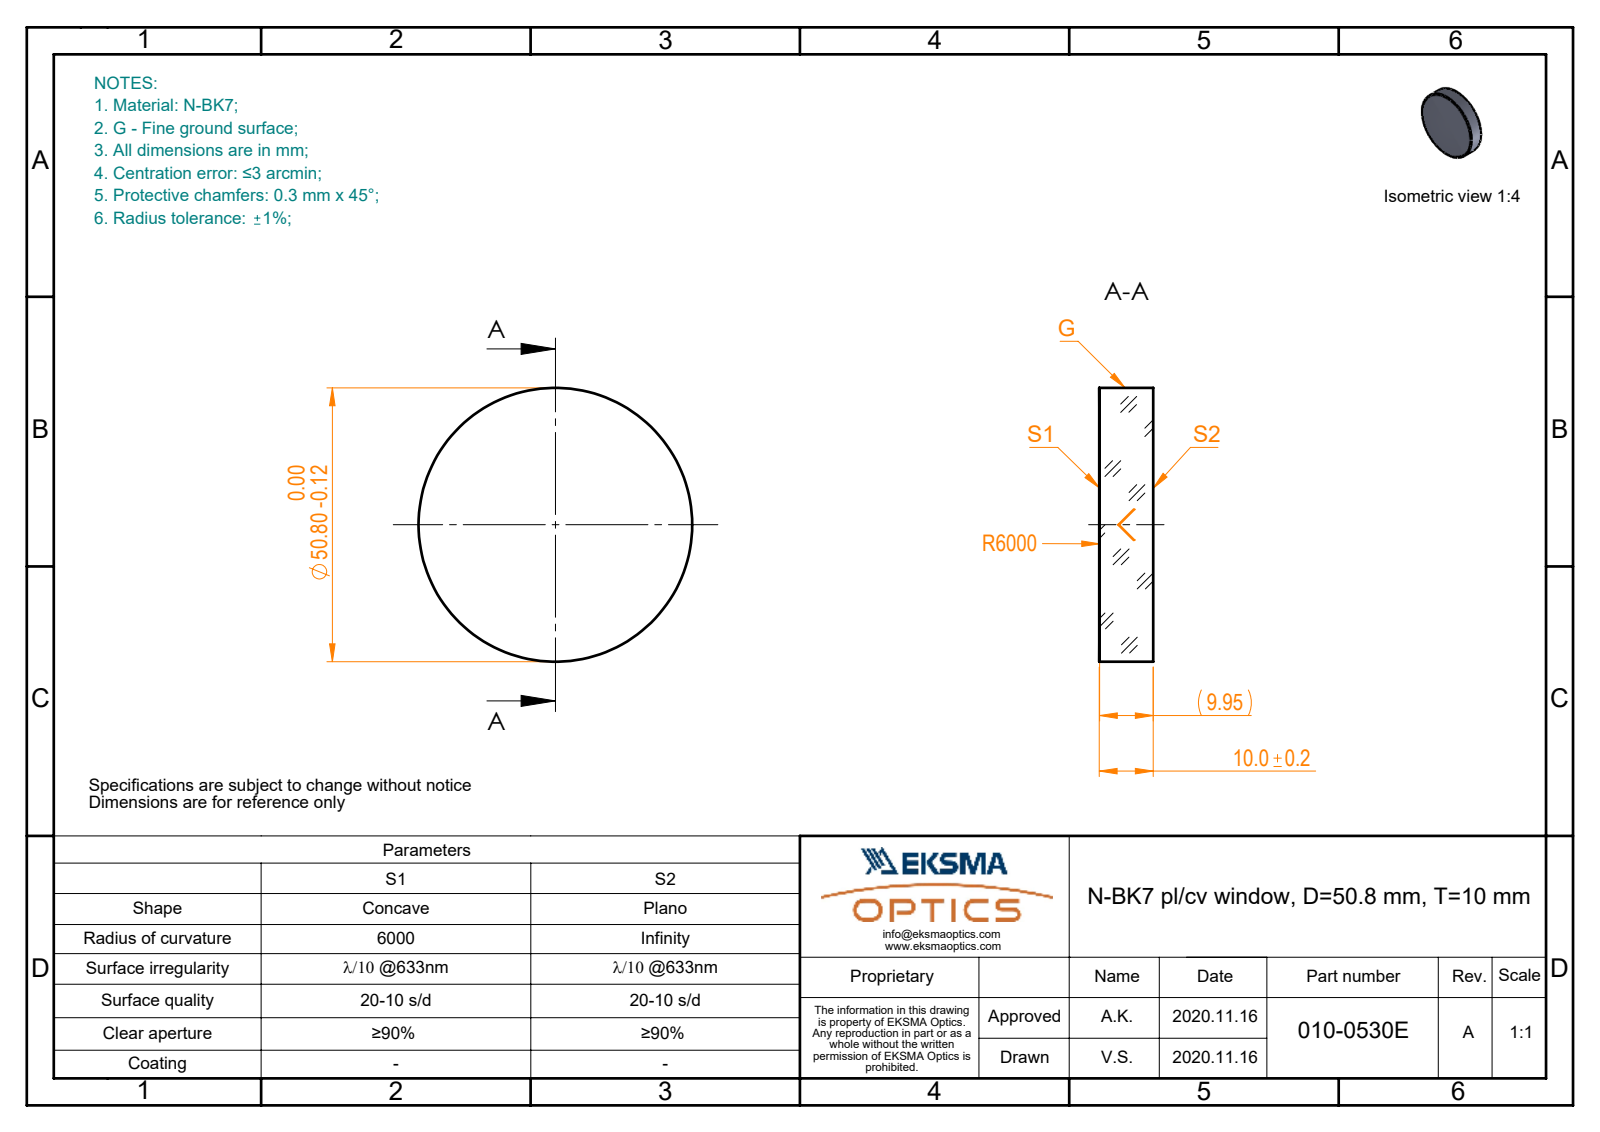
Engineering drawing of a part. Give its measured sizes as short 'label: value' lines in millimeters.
name: 010-0530E_N-BK7_PCV_window
written by: SolidWorks 2019 (CONFIG_CONTROL_DESIGN)
unit: mm
bodies: 1 solid, 5 faces (1 planar, 2 cylindrical, 2 other)
size: 50.8 × 50.8 × 10
volume: 20 214 mm³; area: 5 650 mm²
bosses: 1× ⌀50.8
